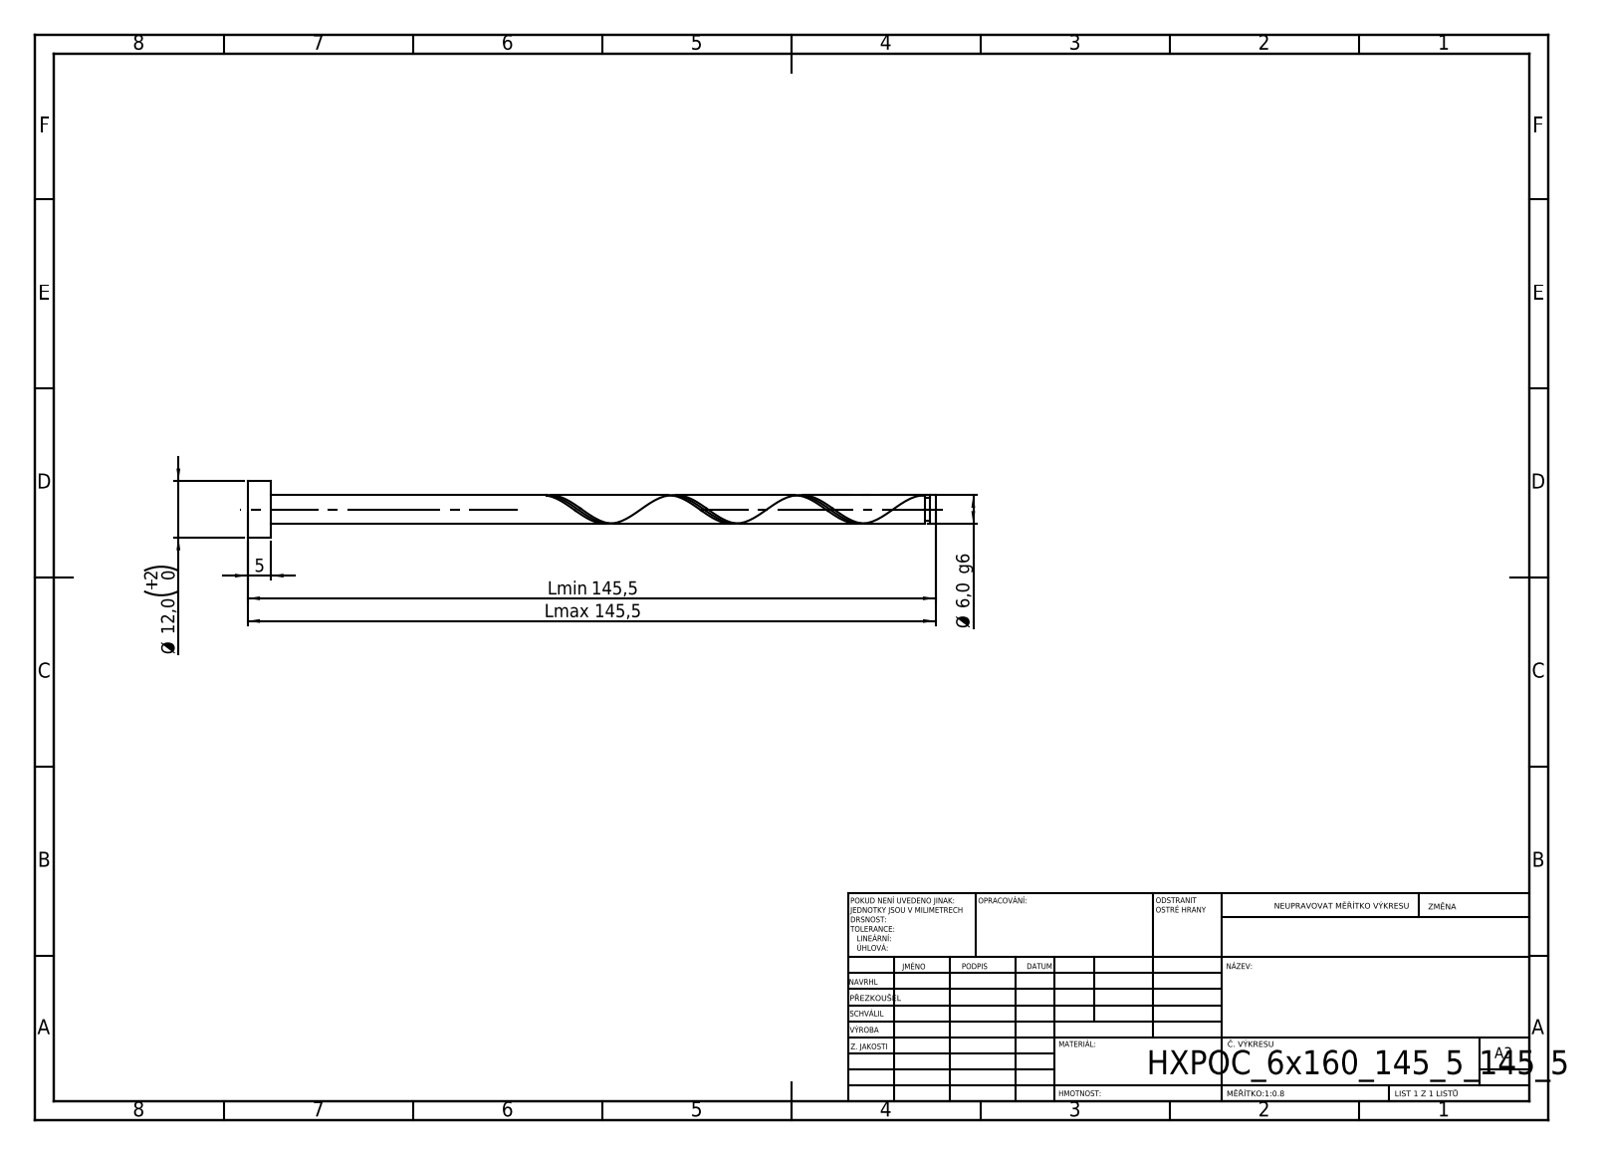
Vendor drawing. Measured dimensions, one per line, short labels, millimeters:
written by: SolidWorks 2019 (CONFIG_CONTROL_DESIGN)
unit: mm
bodies: 1 solid, 21 faces (6 planar, 14 cylindrical, 1 other)
size: 145.5 × 12 × 12
volume: 4 483 mm³; area: 3 139 mm²
bosses: 1× ⌀12, 1× ⌀6, 1× ⌀4.8
face distances: 5, 145.5, 140.5, 144.39, 139.39, 1.11, 143.19, 138.19, 1.2, 2.31
